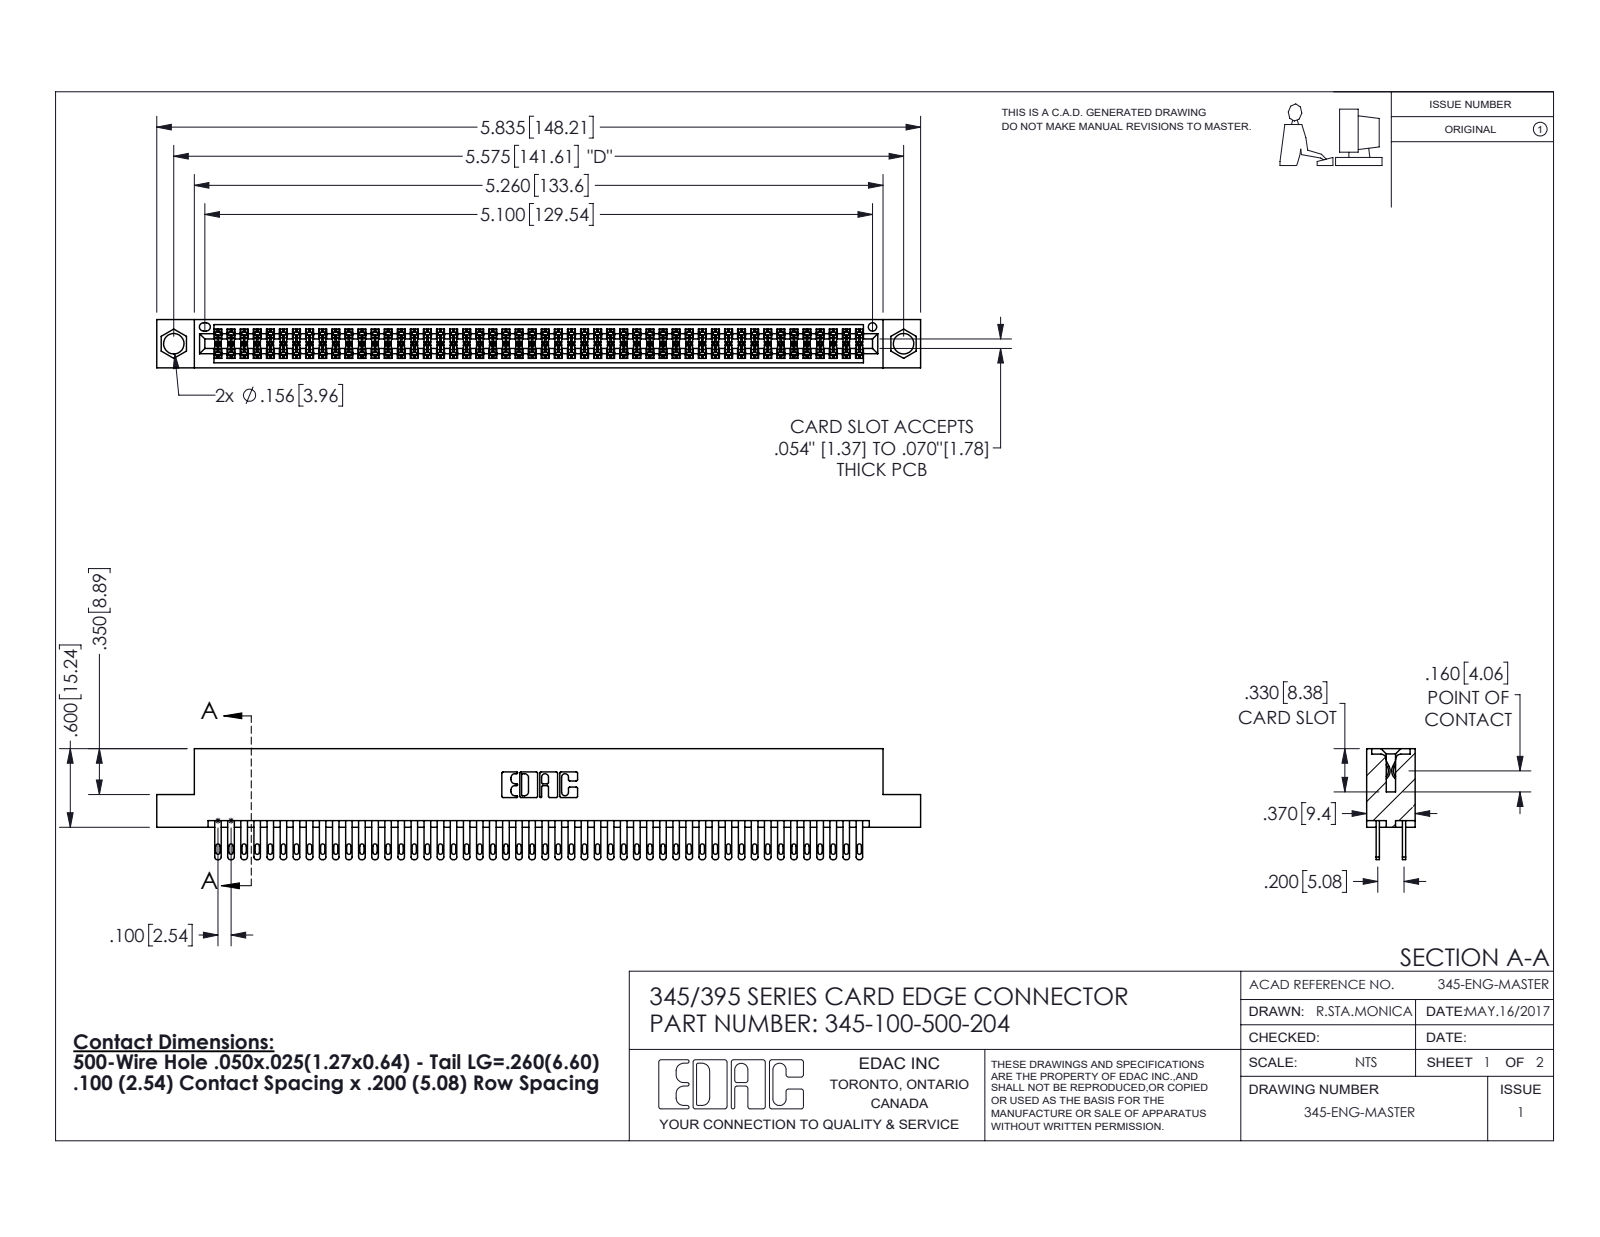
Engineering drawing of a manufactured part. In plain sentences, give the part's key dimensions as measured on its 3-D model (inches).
The part is named "345 Part_Flush Mounting Lugs - 0.156 Dia-TI; 345-100-500-204; 345-292-001_345-293-100". Its 3-D file was written by "SolidWorks 2020 (CONFIG_CONTROL_DESIGN)". It is 101 solids with 4740 faces: 2794 planar, 1946 cylindrical and 0 other. Overall it measures 5.835 by 0.847 by 0.37 inches. Its volume is 0.895 cubic inches and its surface area 35.2 square inches. Round holes: 2 of diameter 0.156, 1 of diameter 0.064. Partial cylindrical surfaces (rounded edges, fillets, slot ends): 150 of radius 0.006, 100 of radius 0.016, 100 of radius 0.02, 22 of radius 0.01, 6 of radius 0.007, 6 of radius 0.031, 3 of radius 0.026, 2 of radius 0.014. The main face-to-face distances are 0.298, 0.072, 0.2, 0.098, 0.272, 0.025, 0.37, 0.225, 0.175, 0.149. The hole center spacings are 0.27, 5.339, 5.575.
